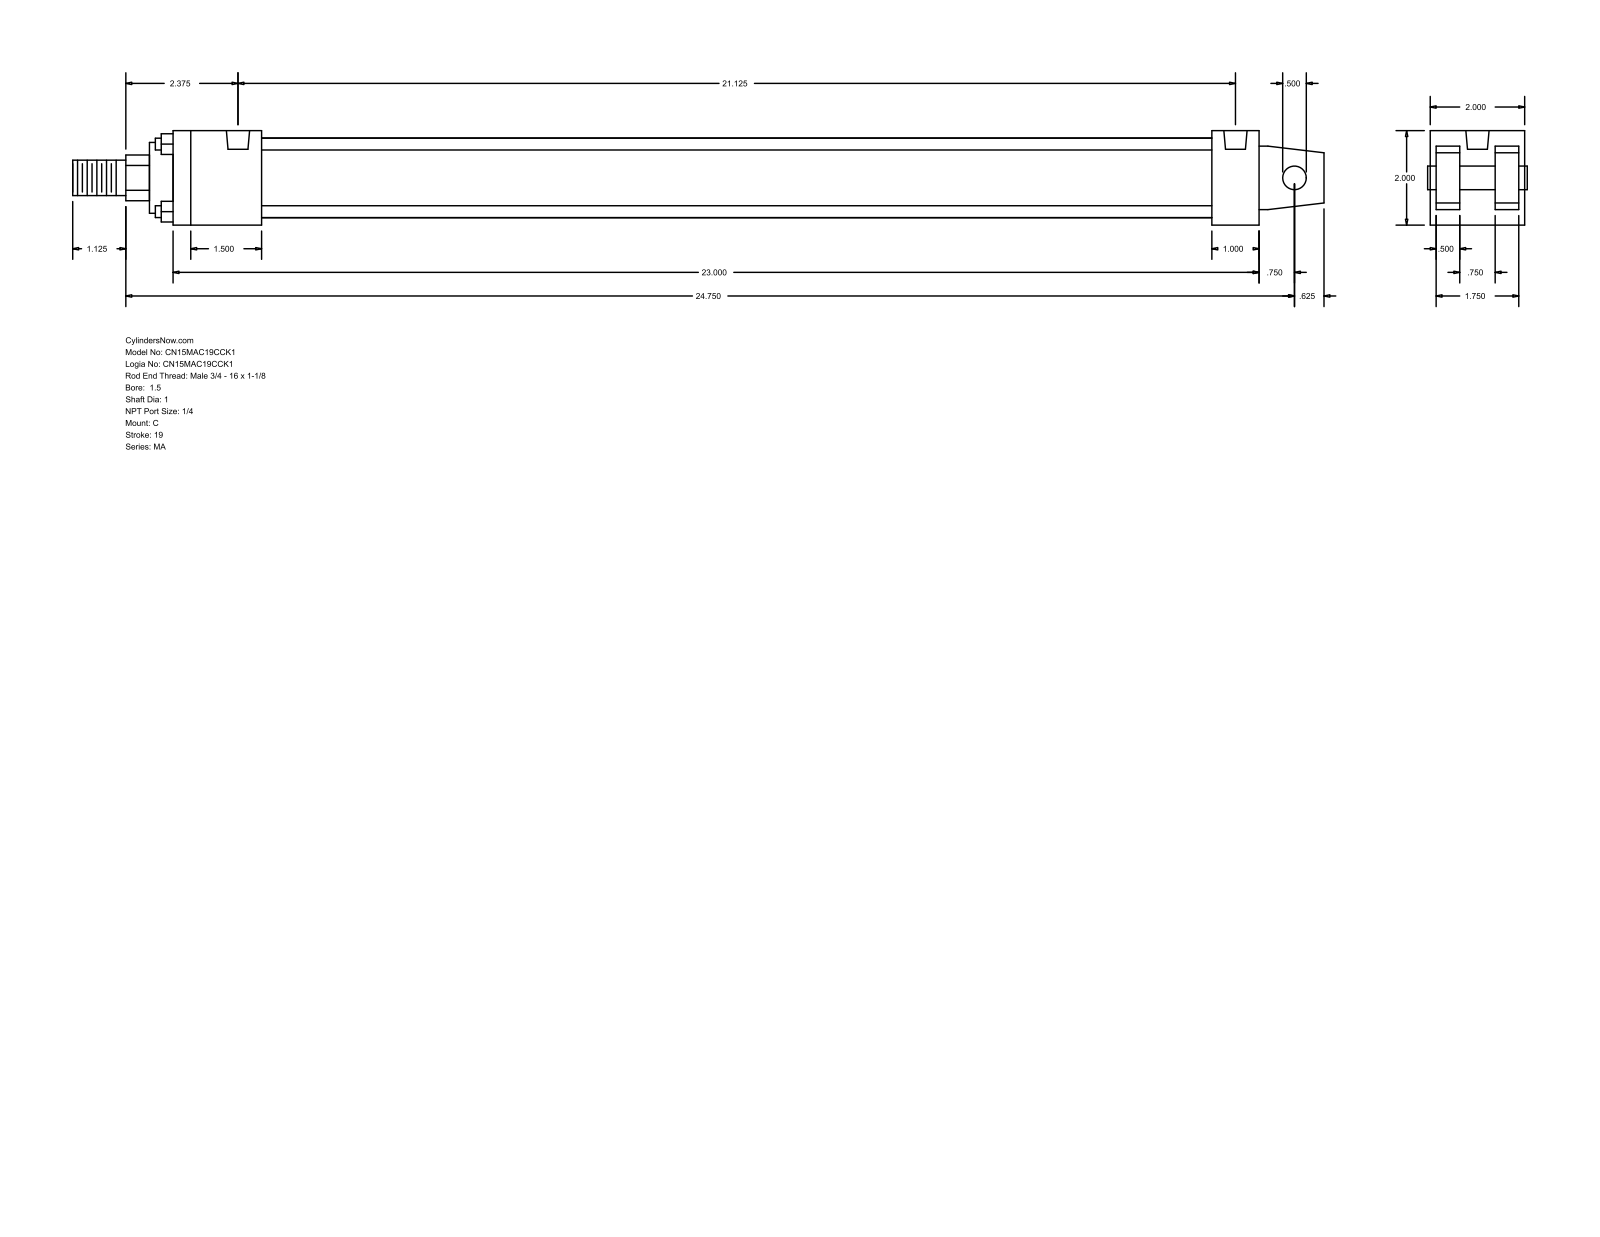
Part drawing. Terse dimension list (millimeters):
name: MA_C__0150_1
written by: GSSL Pune (CONFIG_CONTROL_DESIGN)
unit: mm
bodies: 0 solids, 103 faces (76 planar, 27 cylindrical, 0 other)
size: 673.1 × 50.8 × 50.8
holes: 4× ⌀7.94, 2× ⌀12.49
bosses: 4× ⌀6.35, 1× ⌀42.93, 1× ⌀38.1, 1× ⌀25.4, 1× ⌀19.05, 1× ⌀12.7
rounds: 1× R12.29
face distances: 50.8, 47.63, 12.7, 3.17, 15.87, 34.93, 31.76, 584.2, 25.4, 558.8
hole spacings: 536.57
